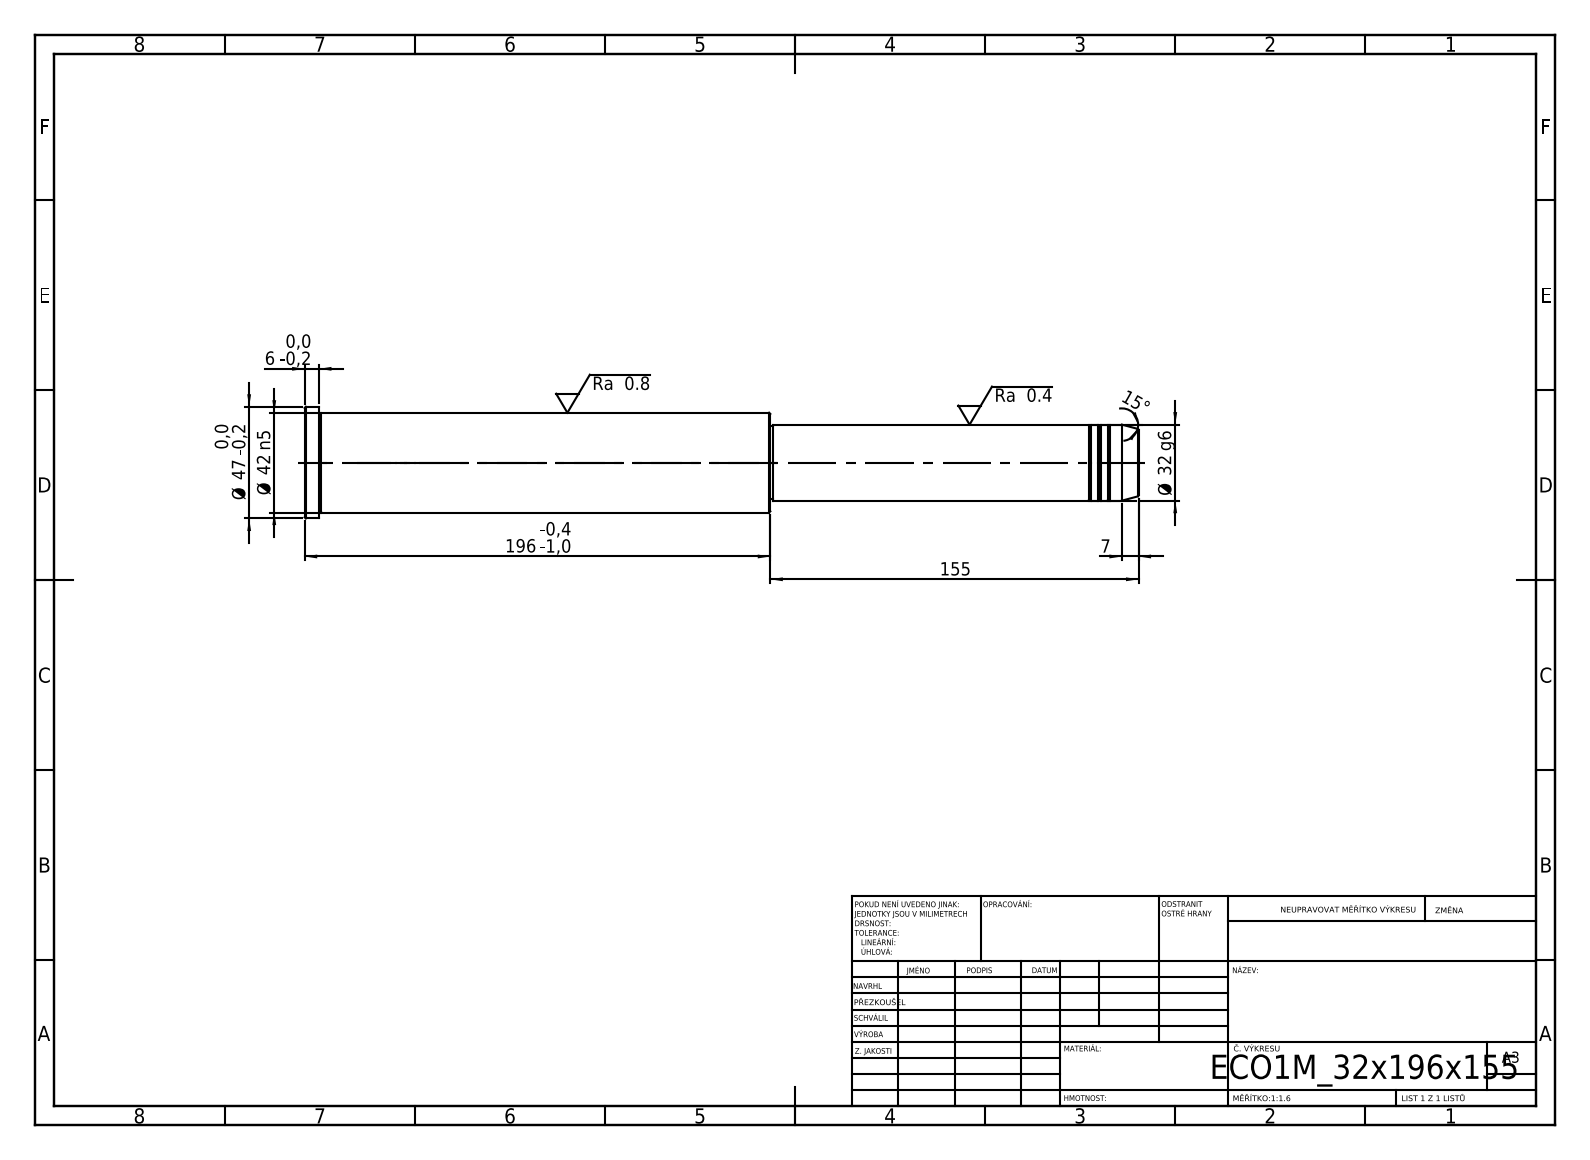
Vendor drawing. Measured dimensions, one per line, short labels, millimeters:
written by: SolidWorks 2019 (CONFIG_CONTROL_DESIGN)
unit: mm
bodies: 1 solid, 43 faces (5 planar, 14 cylindrical, 24 other)
size: 351 × 47 × 47
volume: 397 413 mm³; area: 45 051 mm²
bosses: 1× ⌀47, 1× ⌀42, 1× ⌀32, 1× ⌀31
face distances: 351, 155, 196, 345, 190, 6, 154, 1, 191, 197
